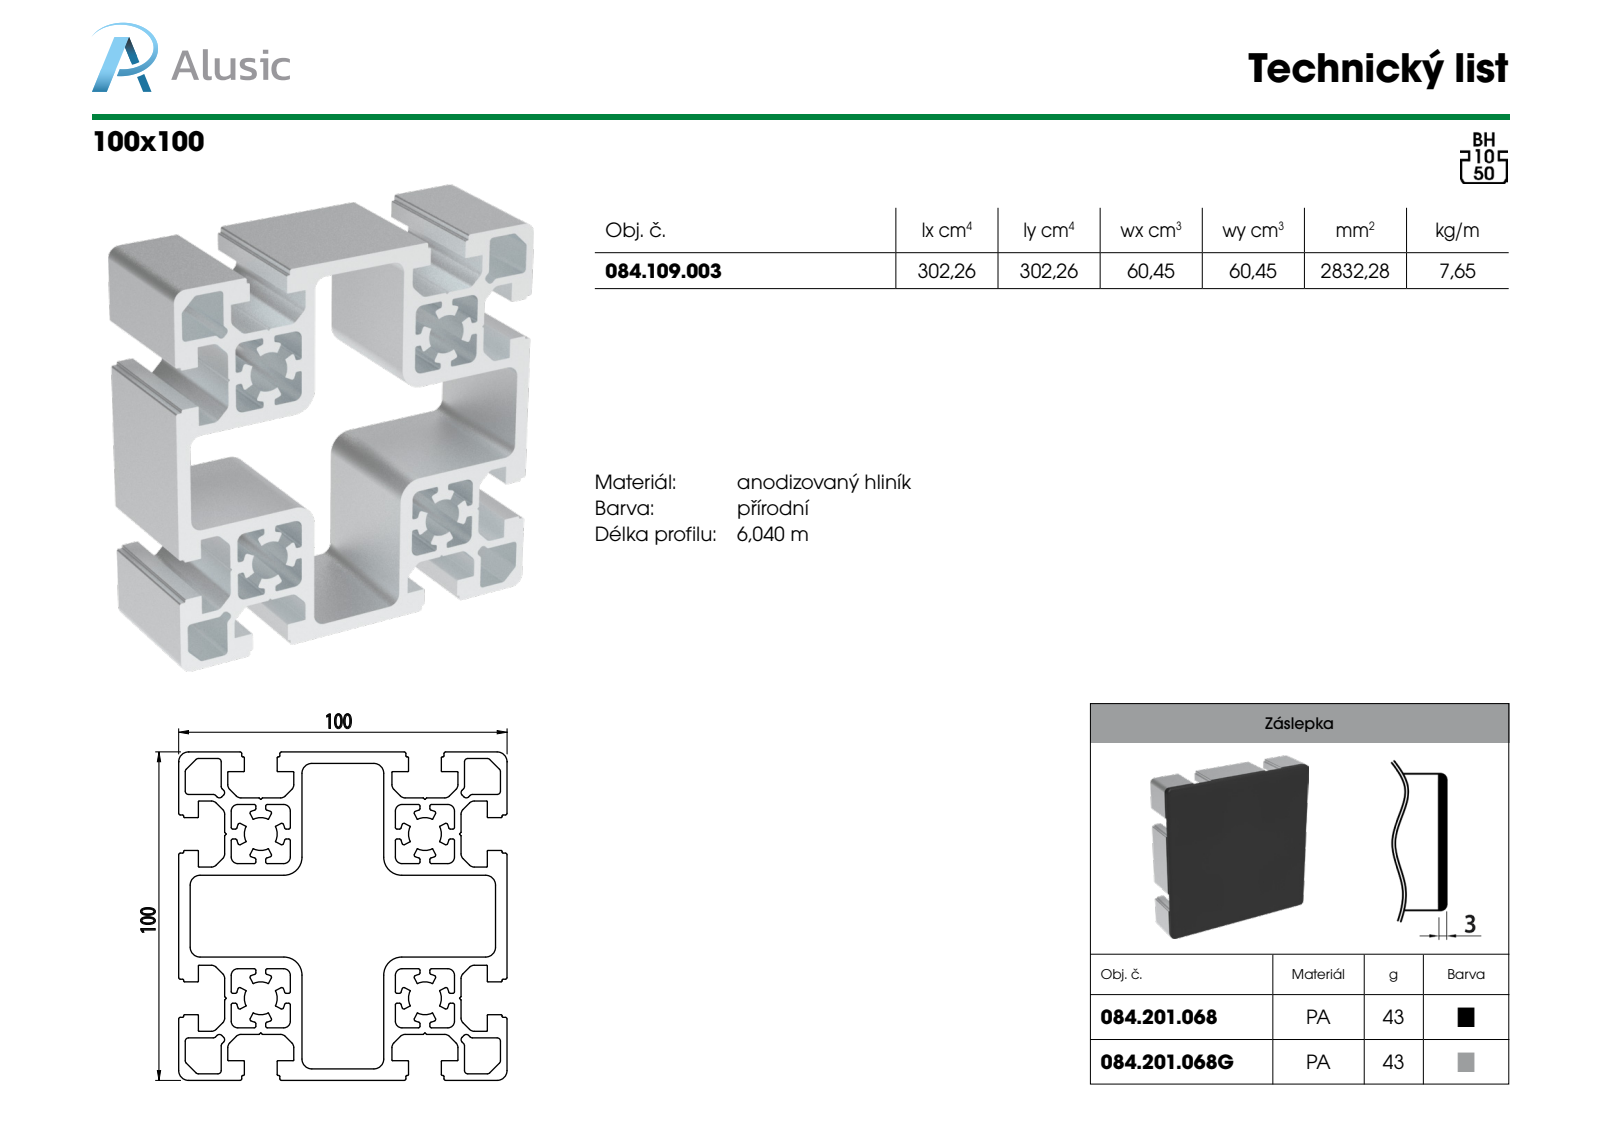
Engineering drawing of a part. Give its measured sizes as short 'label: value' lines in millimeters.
name: 084.109.003
written by: SolidWorks 2018 (AUTOMOTIVE_DESIGN)
unit: mm
bodies: 1 solid, 682 faces (282 planar, 400 cylindrical, 0 other)
size: 100 × 100 × 100
volume: 283 228 mm³; area: 180 364 mm²
rounds: 112× R0.5, 56× R0.1, 48× R2, 32× R0.2, 32× R0.3, 32× R1, 12× R3, 4× R5
face distances: 37.55, 62.45, 14, 100, 2, 84, 24.9, 16, 70, 66
